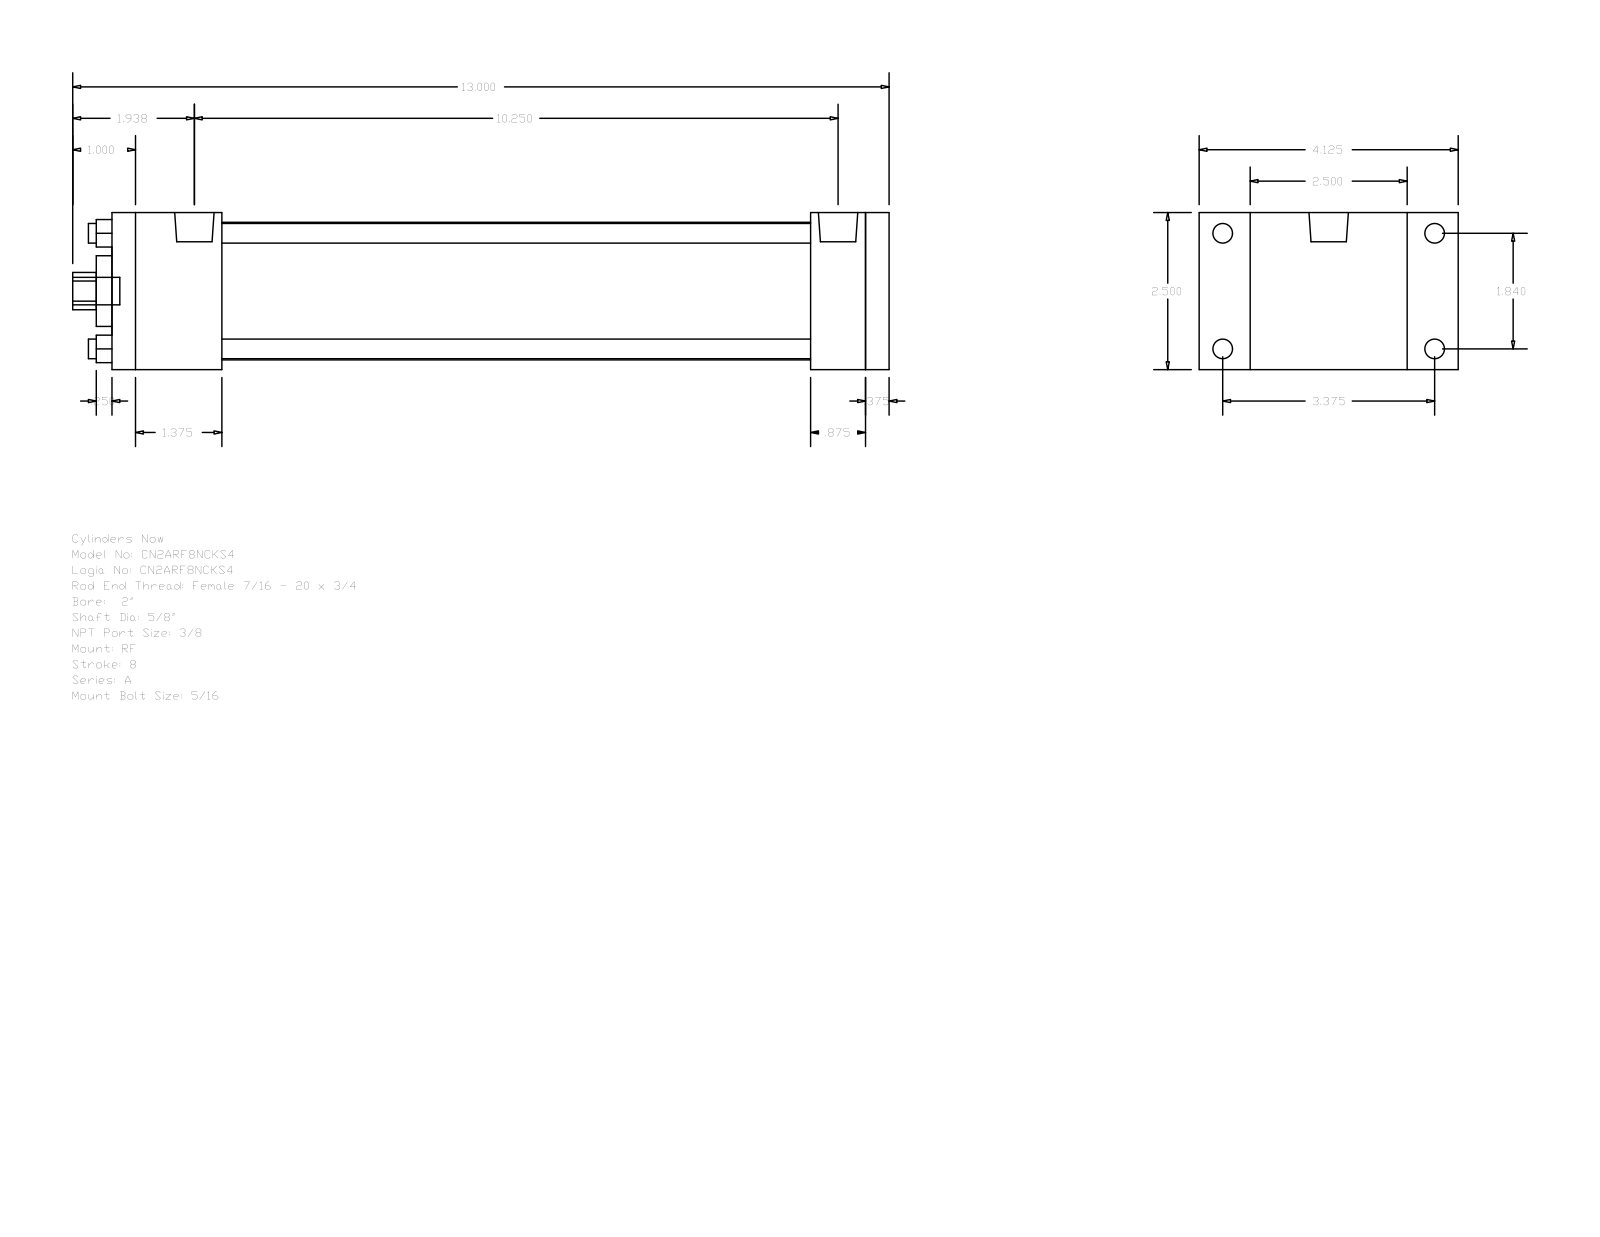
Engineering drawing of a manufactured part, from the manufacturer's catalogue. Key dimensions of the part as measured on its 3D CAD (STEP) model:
Part name (STEP PRODUCT): A_RF__0200_0.625
STEP written by: GSSL Pune (CONFIG_CONTROL_DESIGN)
Units: millimetres
Bodies: 0 solids, 92 faces (64 planar, 28 cylindrical, 0 other)
Overall size (bounding box): 330.2 × 104.78 × 63.5
Round holes (diameter × count): ⌀7.94 ×4, ⌀15.88 ×1, ⌀28.57 ×1, ⌀55.63 ×1
Round bosses / shafts (diameter × count): ⌀7.94 ×4, ⌀5.56 ×4, ⌀15.93 ×2, ⌀11.11 ×1
Partial cylindrical surfaces — rounded edges, fillets, slot ends (radius × count): R7.54 ×1
Main face-to-face distances: 63.5, 314.32, 9.52, 304.8, 44.45, 260.35, 269.87, 282.57, 238.12, 22.23
Hole centre spacings: 33.05, 46.74, 66.1
